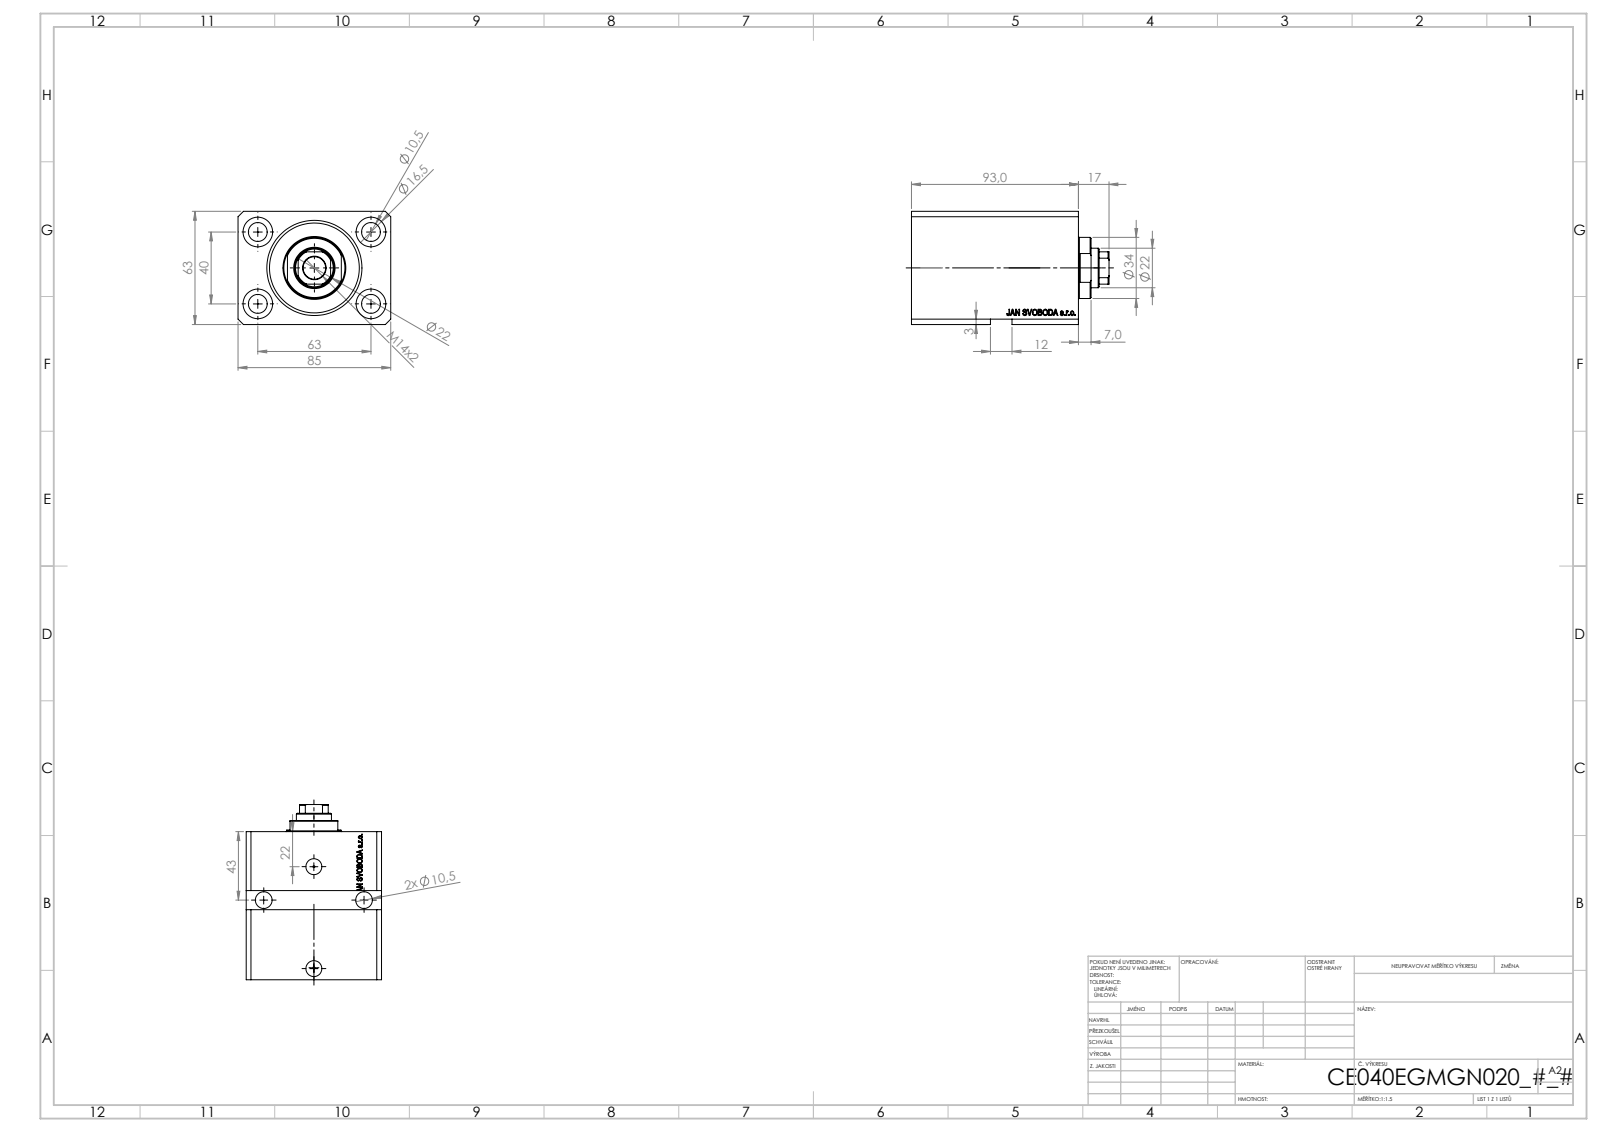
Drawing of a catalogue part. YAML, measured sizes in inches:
part_name: "V250CE_VC_E; V250CE_C_VCP; V250CE_E_Body"
step_written_by: "SolidWorks 2019 (CONFIG_CONTROL_DESIGN)"
units: inches
bodies: {solids: 3, faces: 917, planar: 459, cylindrical: 84, other: 374}
overall_size: [4.327, 3.346, 2.48]
volume: 26.07
surface_area: 138.6
round_holes:
  - {diameter: 0.413, count: 6}
  - {diameter: 0.049, count: 4}
  - {diameter: 0.65, count: 4}
  - {diameter: 0.394, count: 2}
  - {diameter: 0.518, count: 2}
  - {diameter: 0.787, count: 2}
  - {diameter: 0.492, count: 1}
  - {diameter: 0.866, count: 1}
  - {diameter: 1.575, count: 1}
  - {diameter: 2.087, count: 1}
round_bosses_or_shafts:
  - {diameter: 1.339, count: 1}
partial_cylinders:
  - {radius: 0.413, count: 1}
face_to_face_distances: [2.48, 3.346, 3.661, 2.594, 1.067, 0.449, 2.146, 3.213, 0.433, 3.228]
hole_center_spacings: [1.469, 2.48, 1.491, 1.575, 2.082, 2.098, 2.938, 0.021]
